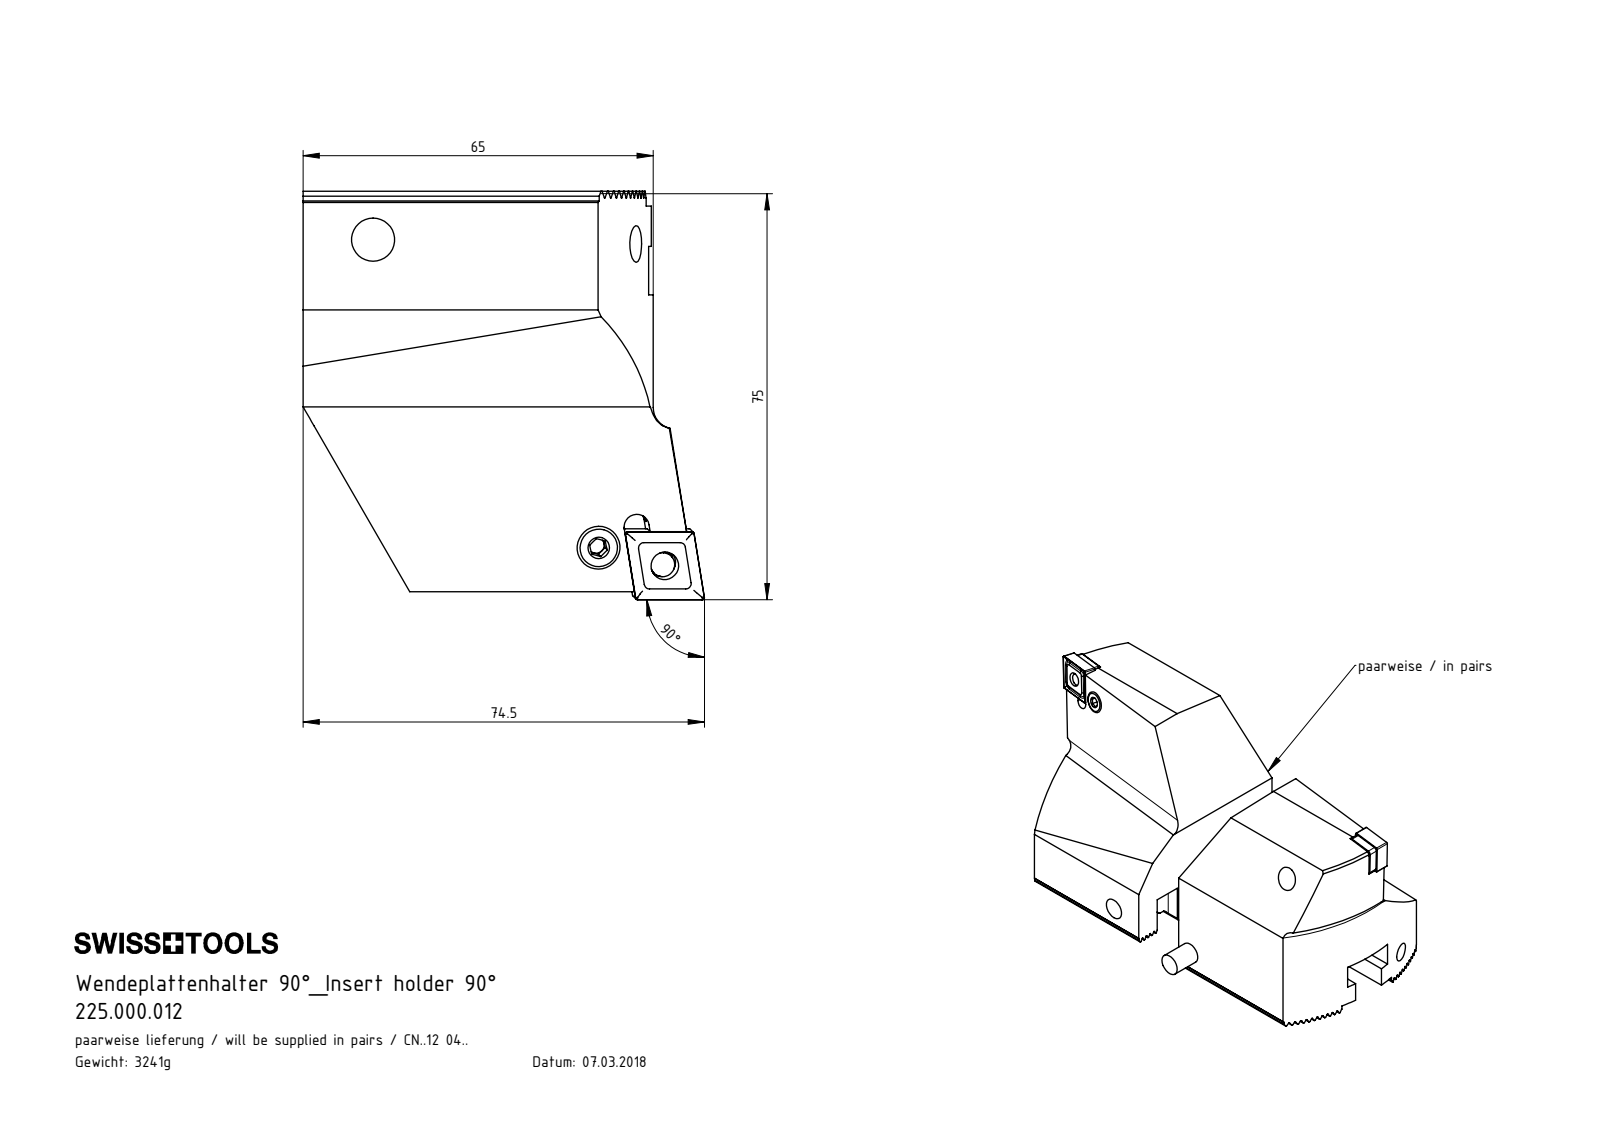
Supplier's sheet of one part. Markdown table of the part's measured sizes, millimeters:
| quantity | value |
| --- | --- |
| part name | WCD-ER2.101.003_A; WCD-ER1.101.000; WCD-ER3.101.000_A; WCD (+6 more) |
| STEP written by | SolidWorks 2017 (CONFIG_CONTROL_DESIGN) |
| units | millimeters |
| bodies | 16 solids, 1263 faces (759 planar, 164 cylindrical, 340 other) |
| overall size | 205.01 × 94 × 75.79 |
| volume | 413 723 mm³ |
| surface area | 67 086 mm² |
| round holes (diameter × count) | 8 × 4, 5.16 × 2, 6.4 × 2, 6.8 × 2, 7 × 2, 8.4 × 2 |
| round bosses / shafts (diameter × count) | 8 × 3, 7.9 × 2, 6.4 × 2, 4.5 × 2, 3.55 × 2, 5.5 × 1 |
| partial cylindrical surfaces (radius × count) | 0.14 × 22, 0.4 × 8, 1 × 8, 2.5 × 6, 2.1 × 2, 2.2 × 2, 2.35 × 2, 2.8 × 2 |
| main face-to-face distances | 1.73, 8.66, 3.46, 70, 6.93, 5.2, 43.3, 24.5, 45.5, 10.39 |
| hole center spacings | 7, 12.8, 12.86, 75, 40, 68, 82 |
